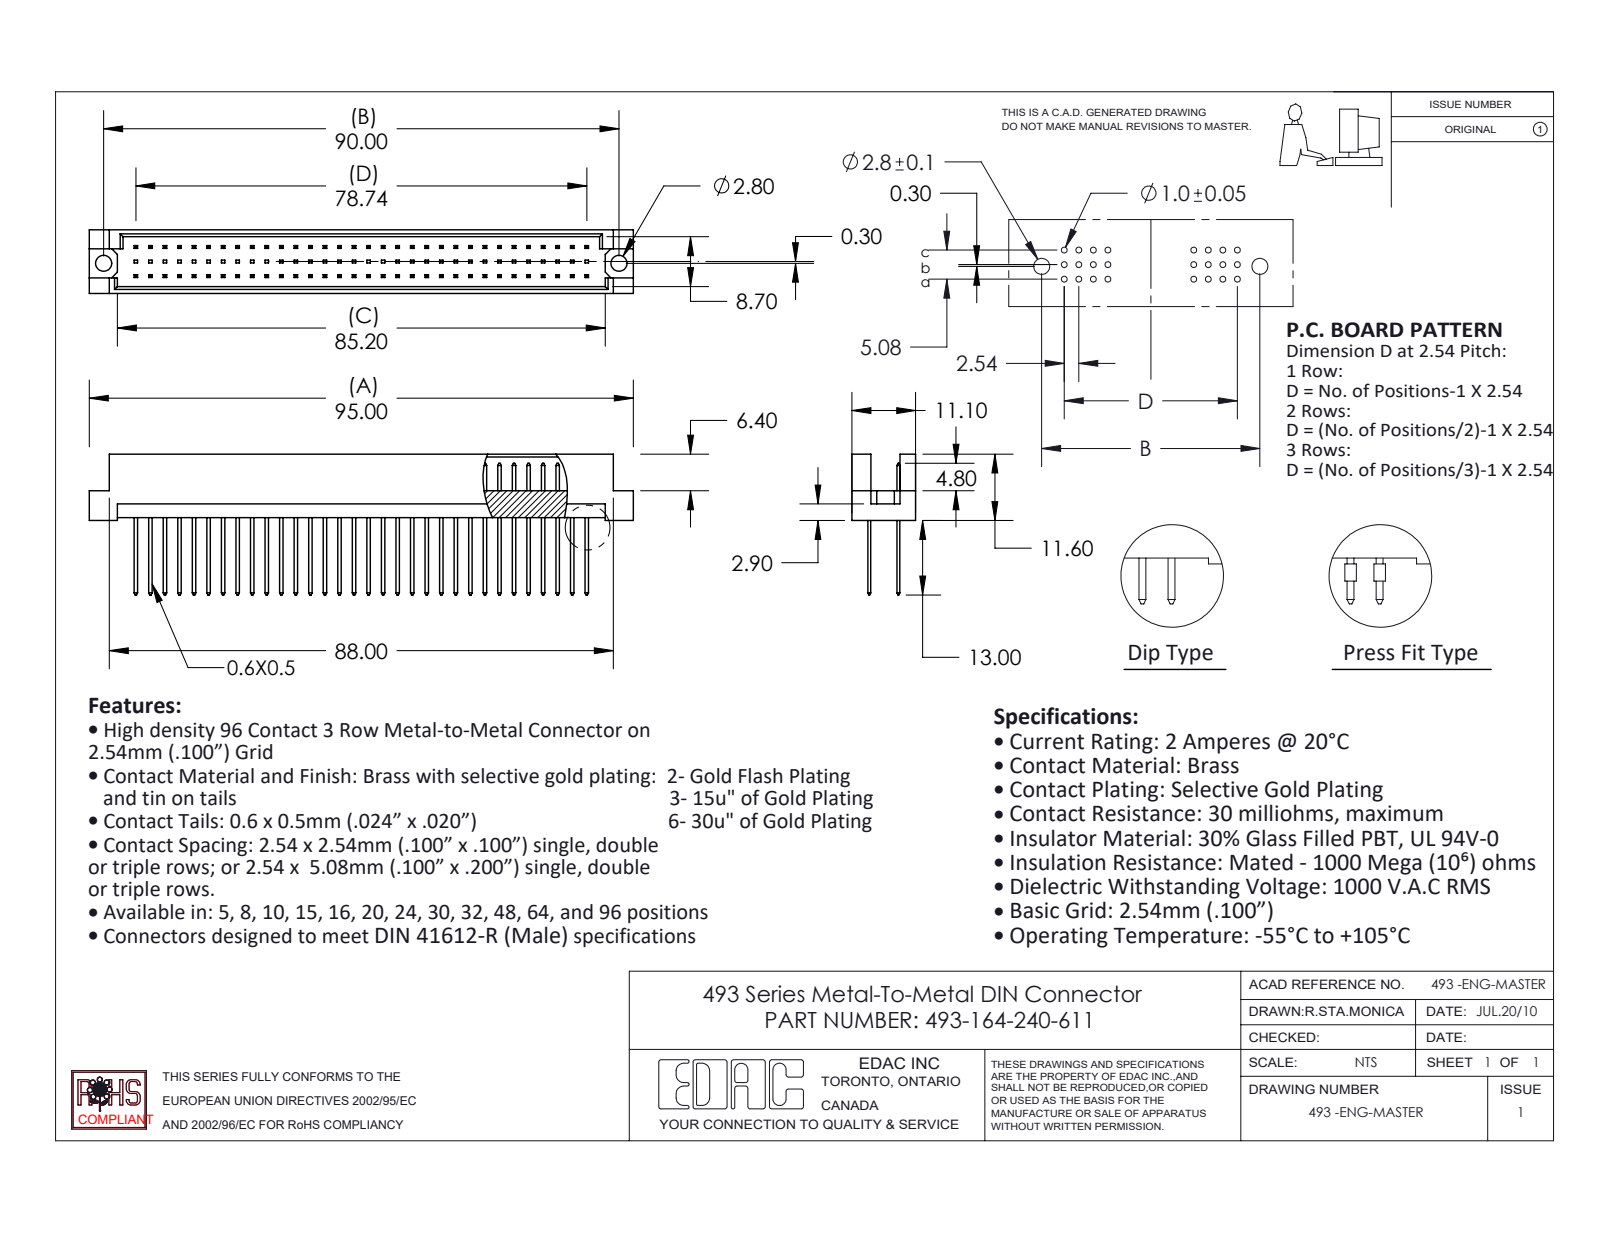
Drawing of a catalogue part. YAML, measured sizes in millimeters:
part_name: "493-164-240-611; 493 Part_96; 493-290_40"
step_written_by: "SolidWorks 2020 (CONFIG_CONTROL_DESIGN)"
units: millimeters
bodies: {solids: 65, faces: 1332, planar: 1328, cylindrical: 4, other: 0}
overall_size: [95, 24.6, 11.1]
volume: 6093
surface_area: 9688
round_holes:
  - {diameter: 2.8, count: 2}
face_to_face_distances: [5.08, 1.2, 9.9, 0.5, 2.76, 3.26, 7.84, 8.34, 1.56, 2.06]
hole_center_spacings: [90]
